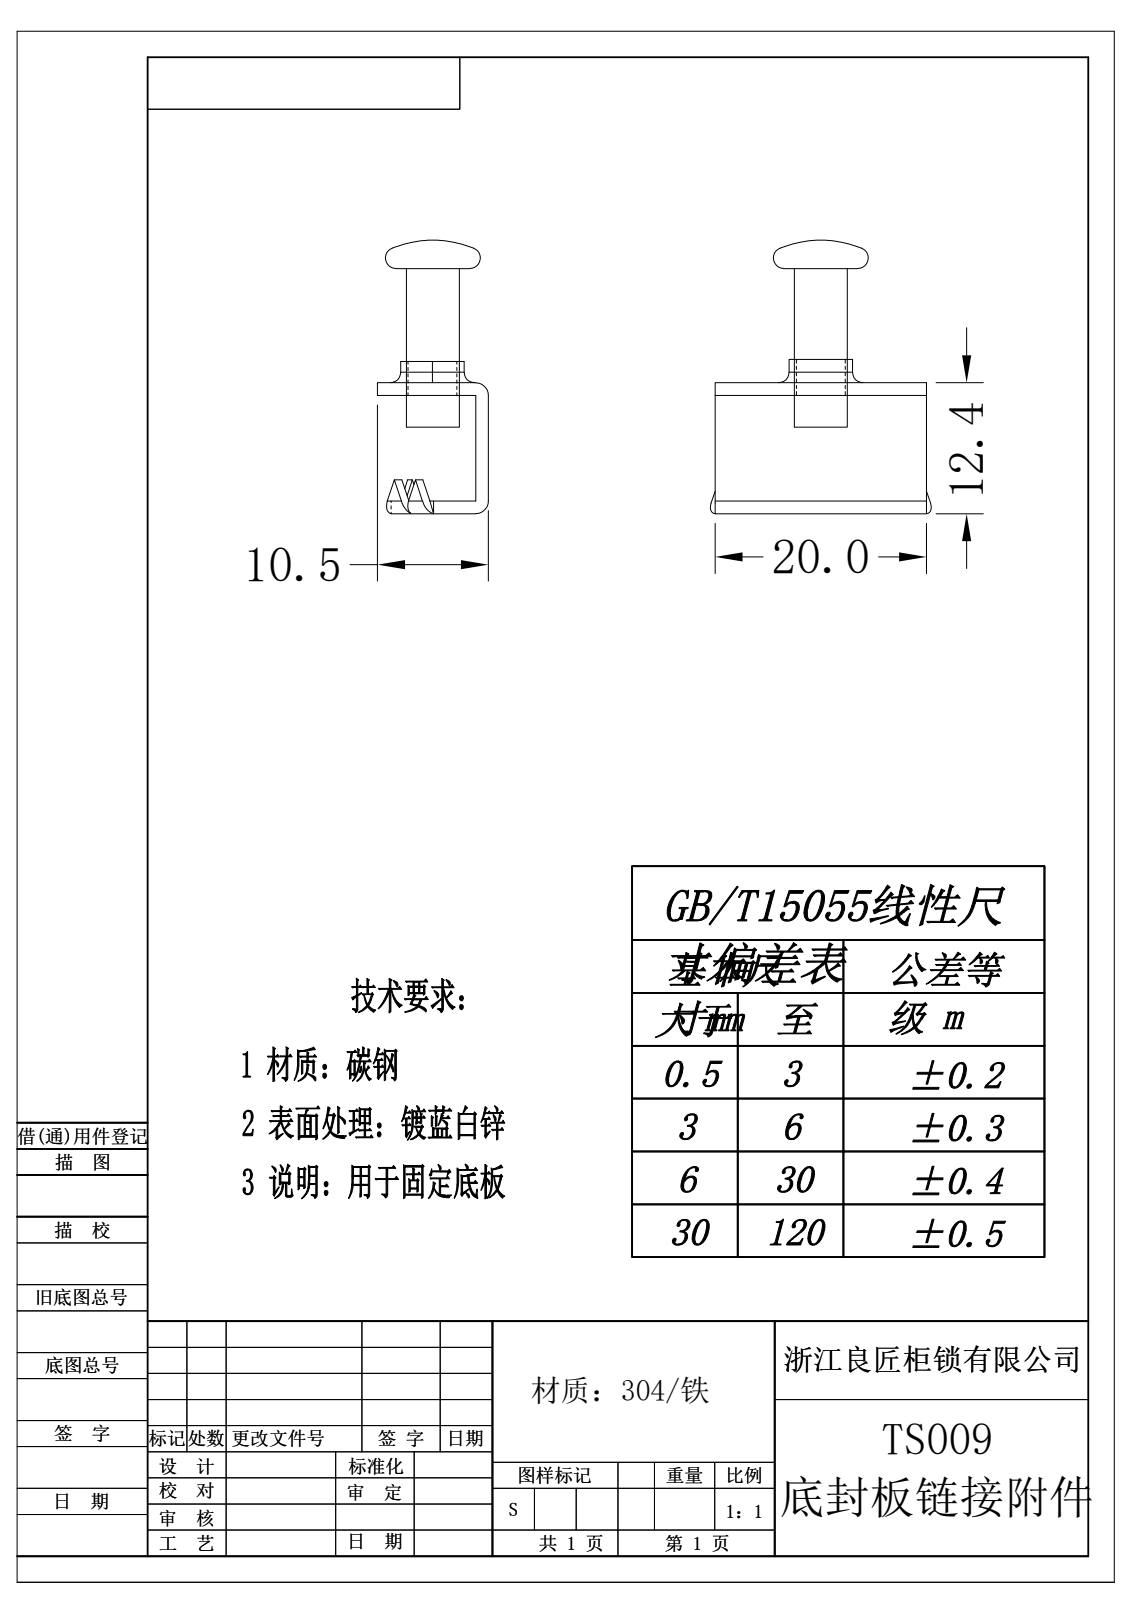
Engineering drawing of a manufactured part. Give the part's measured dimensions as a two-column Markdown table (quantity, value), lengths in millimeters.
| quantity | value |
| --- | --- |
| STEP written by | Rhino 8.5 (CONFIG_CONTROL_DESIGN) |
| units | millimeters |
| bodies | 2 solids, 242 faces (54 planar, 106 cylindrical, 82 other) |
| overall size | 22.78 × 21.26 × 10.71 |
| volume | 1 067 mm³ |
| surface area | 1 946 mm² |
| round holes (diameter × count) | 4.6 × 1 |
| round bosses / shafts (diameter × count) | 6 × 1, 4.07 × 1 |
| partial cylindrical surfaces (radius × count) | 0.1 × 24, 0.5 × 8, 1.2 × 8, 0.3 × 6 |
| main face-to-face distances | 1.2, 11.2, 10, 12.4, 20, 20.27, 19.07, 9.07, 7.87, 10.5 |
